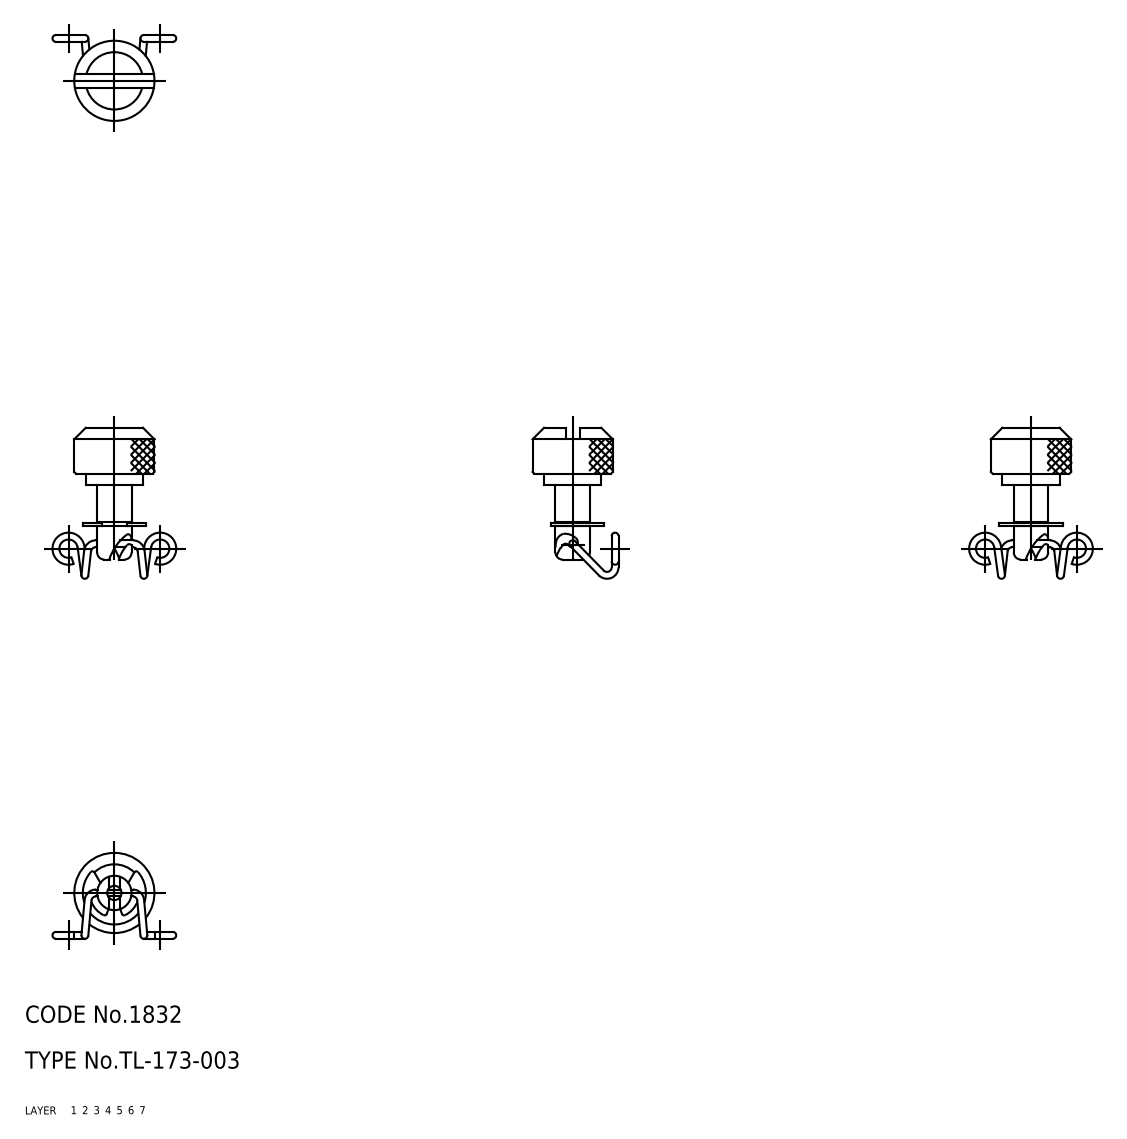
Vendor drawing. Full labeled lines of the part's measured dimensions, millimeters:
Part name (STEP PRODUCT): spring; retainer; fastener; TL_173_003_19405_36
STEP written by: CADfix (AUTOMOTIVE_DESIGN)
Units: millimetres
Bodies: 3 solids, 86 faces (0 planar, 0 cylindrical, 86 other)
Overall size (bounding box): 26.3 × 21.6 × 15
Volume: 1 617 mm³ · Surface area: 1 338 mm²
